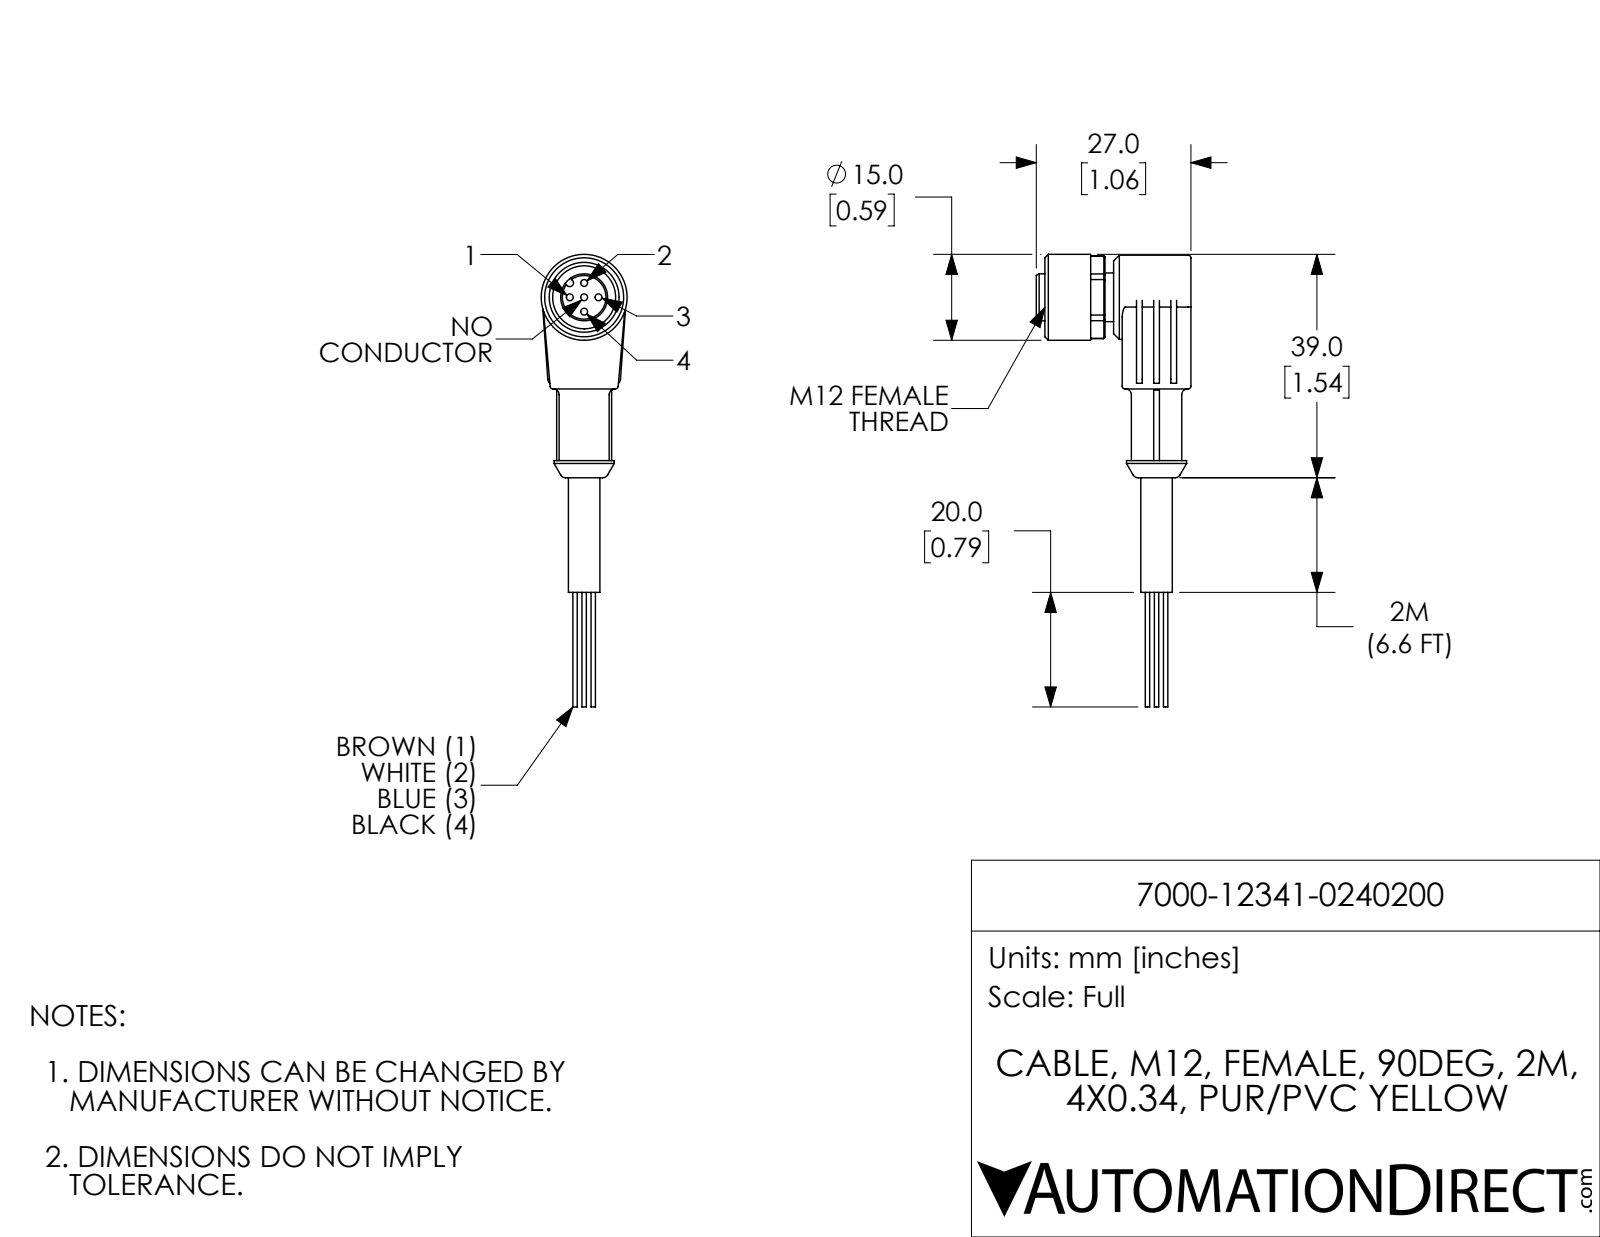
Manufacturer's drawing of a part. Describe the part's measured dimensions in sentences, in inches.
The part is named "7000-12341-0240200". Its 3-D file was written by "SolidWorks 2017 (AUTOMOTIVE_DESIGN)". It is 1 solid with 152 faces: 65 planar, 59 cylindrical and 28 other. Overall it measures 3.11 by 1.063 by 0.591 inches. Its volume is 0.417 cubic inches and its surface area 5.896 square inches. Round holes: 5 of diameter 0.047, 1 of diameter 0.189, 1 of diameter 0.433. Round bosses or shafts: 4 of diameter 0.03, 1 of diameter 0.591, 1 of diameter 0.579, 1 of diameter 0.413, 1 of diameter 0.346, 1 of diameter 0.335, 1 of diameter 0.323, 1 of diameter 0.217. Partial cylindrical surfaces (rounded edges, fillets, slot ends): 8 of radius 0.02, 2 of radius 0.039, 1 of radius 0.026, 1 of radius 0.283. The main face-to-face distances are 0.472, 0.059, 0.118, 0.531, 0.591, 0.217, 0.374, 0.236, 0.315, 0.492. The hole center spacings are 0.098, 0.139, 0.197.
